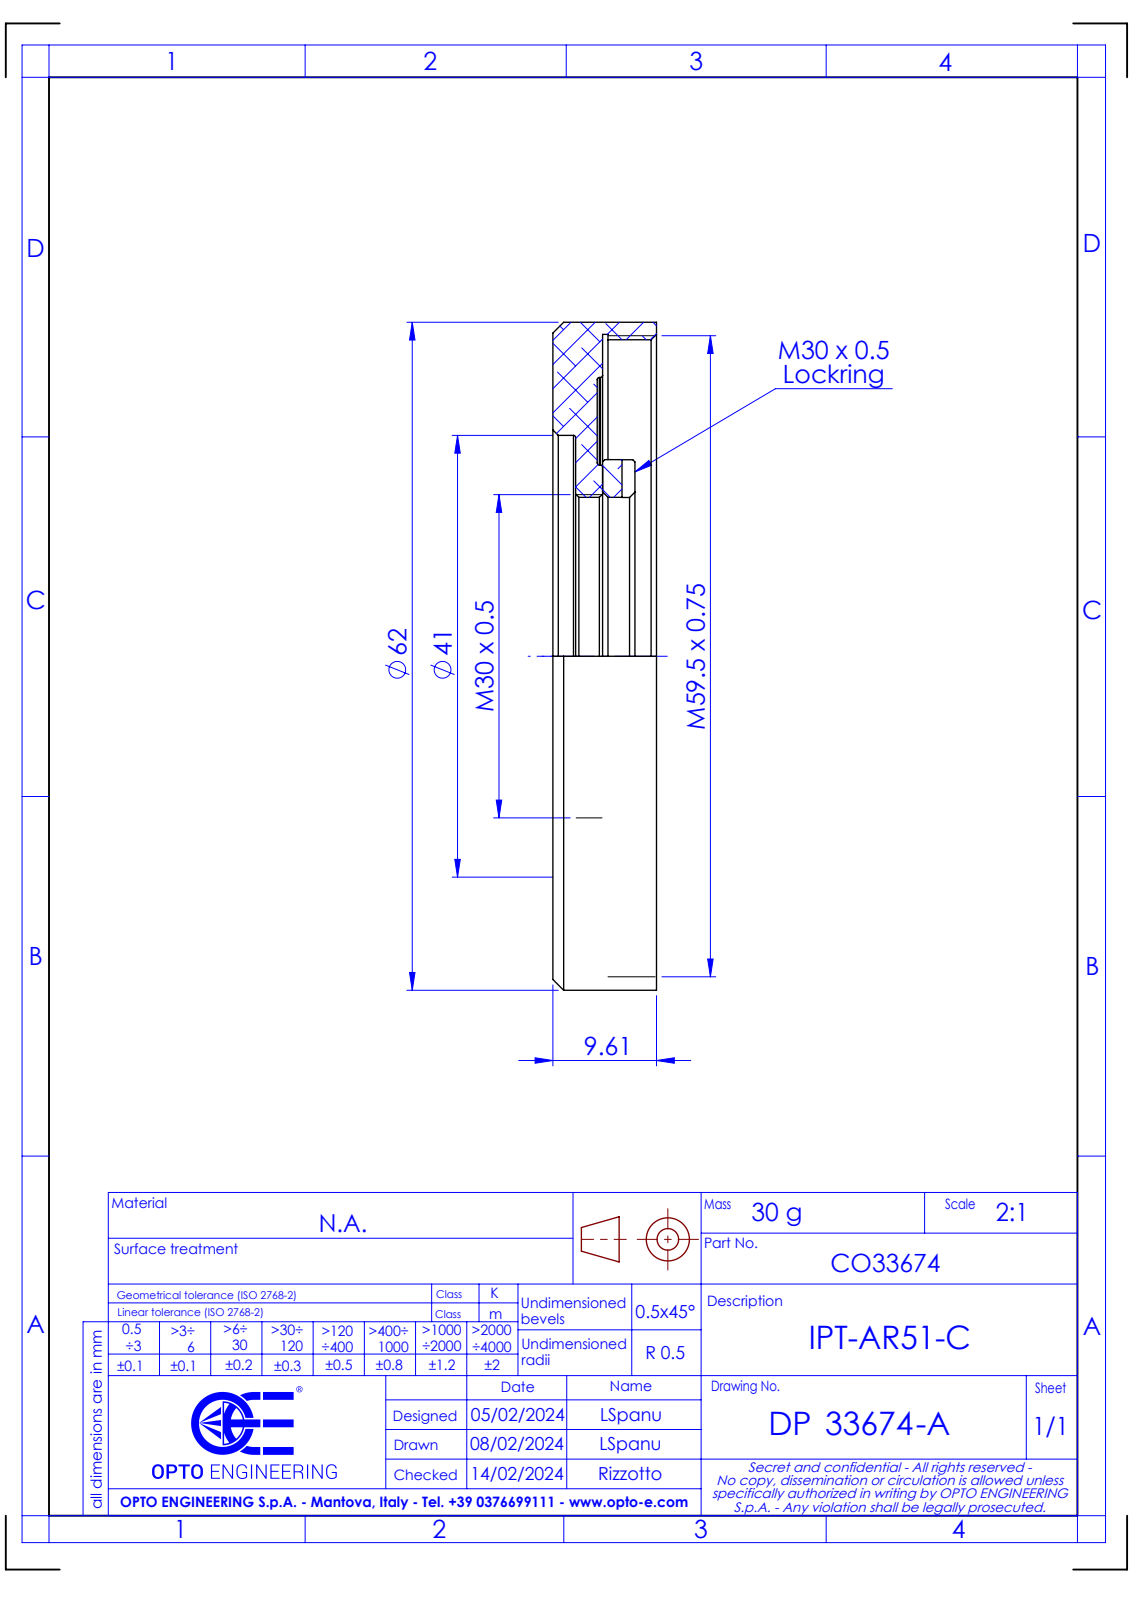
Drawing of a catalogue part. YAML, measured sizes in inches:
part_name: "DP33674-A_IPT-AR51-C"
step_written_by: "SolidWorks 2021 (CONFIG_CONTROL_DESIGN)"
units: inches
bodies: {solids: 0, faces: 58, planar: 14, cylindrical: 18, other: 26}
overall_size: [2.441, 2.441, 0.378]
round_holes:
  - {diameter: 1.161, count: 1}
  - {diameter: 1.614, count: 1}
  - {diameter: 2.037, count: 1}
  - {diameter: 2.313, count: 1}
  - {diameter: 2.352, count: 1}
round_bosses_or_shafts:
  - {diameter: 2.441, count: 1}
  - {diameter: 1.437, count: 1}
  - {diameter: 1.398, count: 1}
face_to_face_distances: [0.162, 0.181, 0.02, 0.079, 0.083, 0.098, 0.217, 0.3, 0.138, 0.118]
